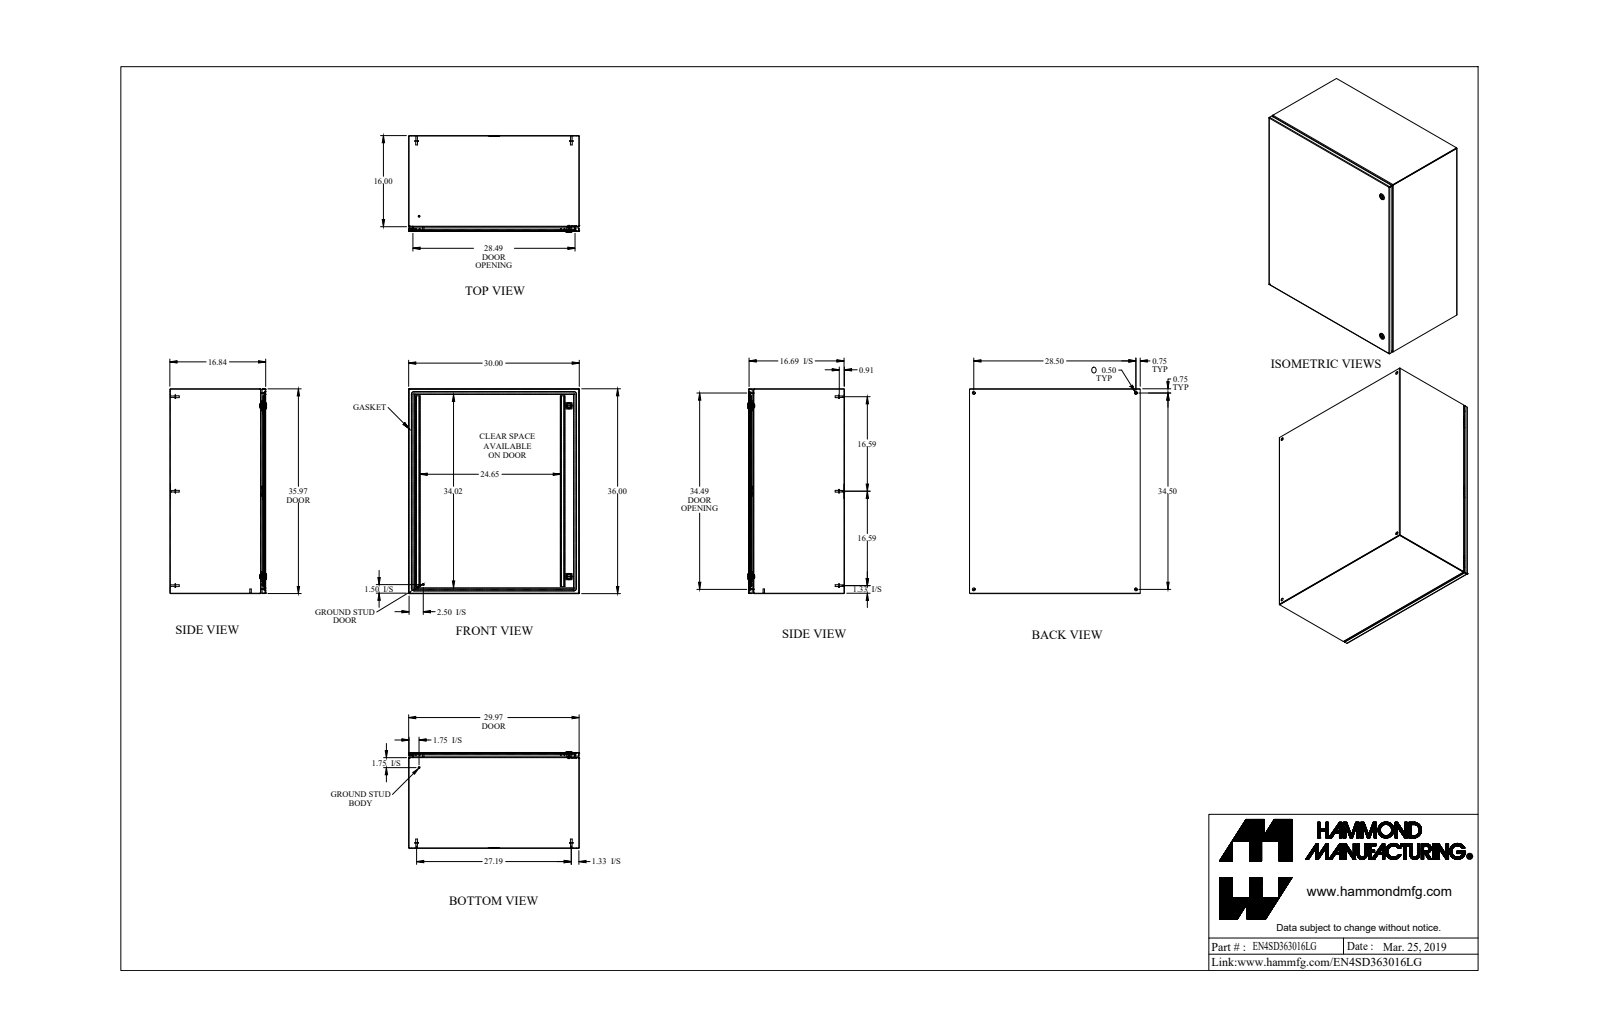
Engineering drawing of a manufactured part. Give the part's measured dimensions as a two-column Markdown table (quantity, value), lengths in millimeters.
| quantity | value |
| --- | --- |
| part name | EN4SD363016LG |
| STEP written by | SolidWorks 2019 (AUTOMOTIVE_DESIGN) |
| units | millimeters |
| bodies | 35 solids, 900 faces (434 planar, 294 cylindrical, 172 other) |
| overall size | 914.4 × 762 × 431.7 |
| volume | 5 622 000 mm³ |
| surface area | 6 201 000 mm² |
| round holes (diameter × count) | 12.7 × 4, 5.9 × 2, 15.9 × 2, 19.9 × 2, 4.4 × 1, 6.1 × 1, 6.1 × 1 |
| round bosses / shafts (diameter × count) | 15.9 × 6, 8 × 6, 6.9 × 6, 27.9 × 2, 13.3 × 2, 7.1 × 2, 6.4 × 2, 11.6 × 1 |
| partial cylindrical surfaces (radius × count) | 0.9 × 18, 2.7 × 18, 1.1 × 12, 2.1 × 12, 7.9 × 12, 0.2 × 6, 1.6 × 6, 3.2 × 4 |
| main face-to-face distances | 1.8, 425.8, 760.2, 424, 427.7, 912.6, 758.3, 762, 910.7, 914.4 |
| hole center spacings | 699, 723.9, 876.3, 1136.6, 63.3, 63.3, 762, 819.6 |
